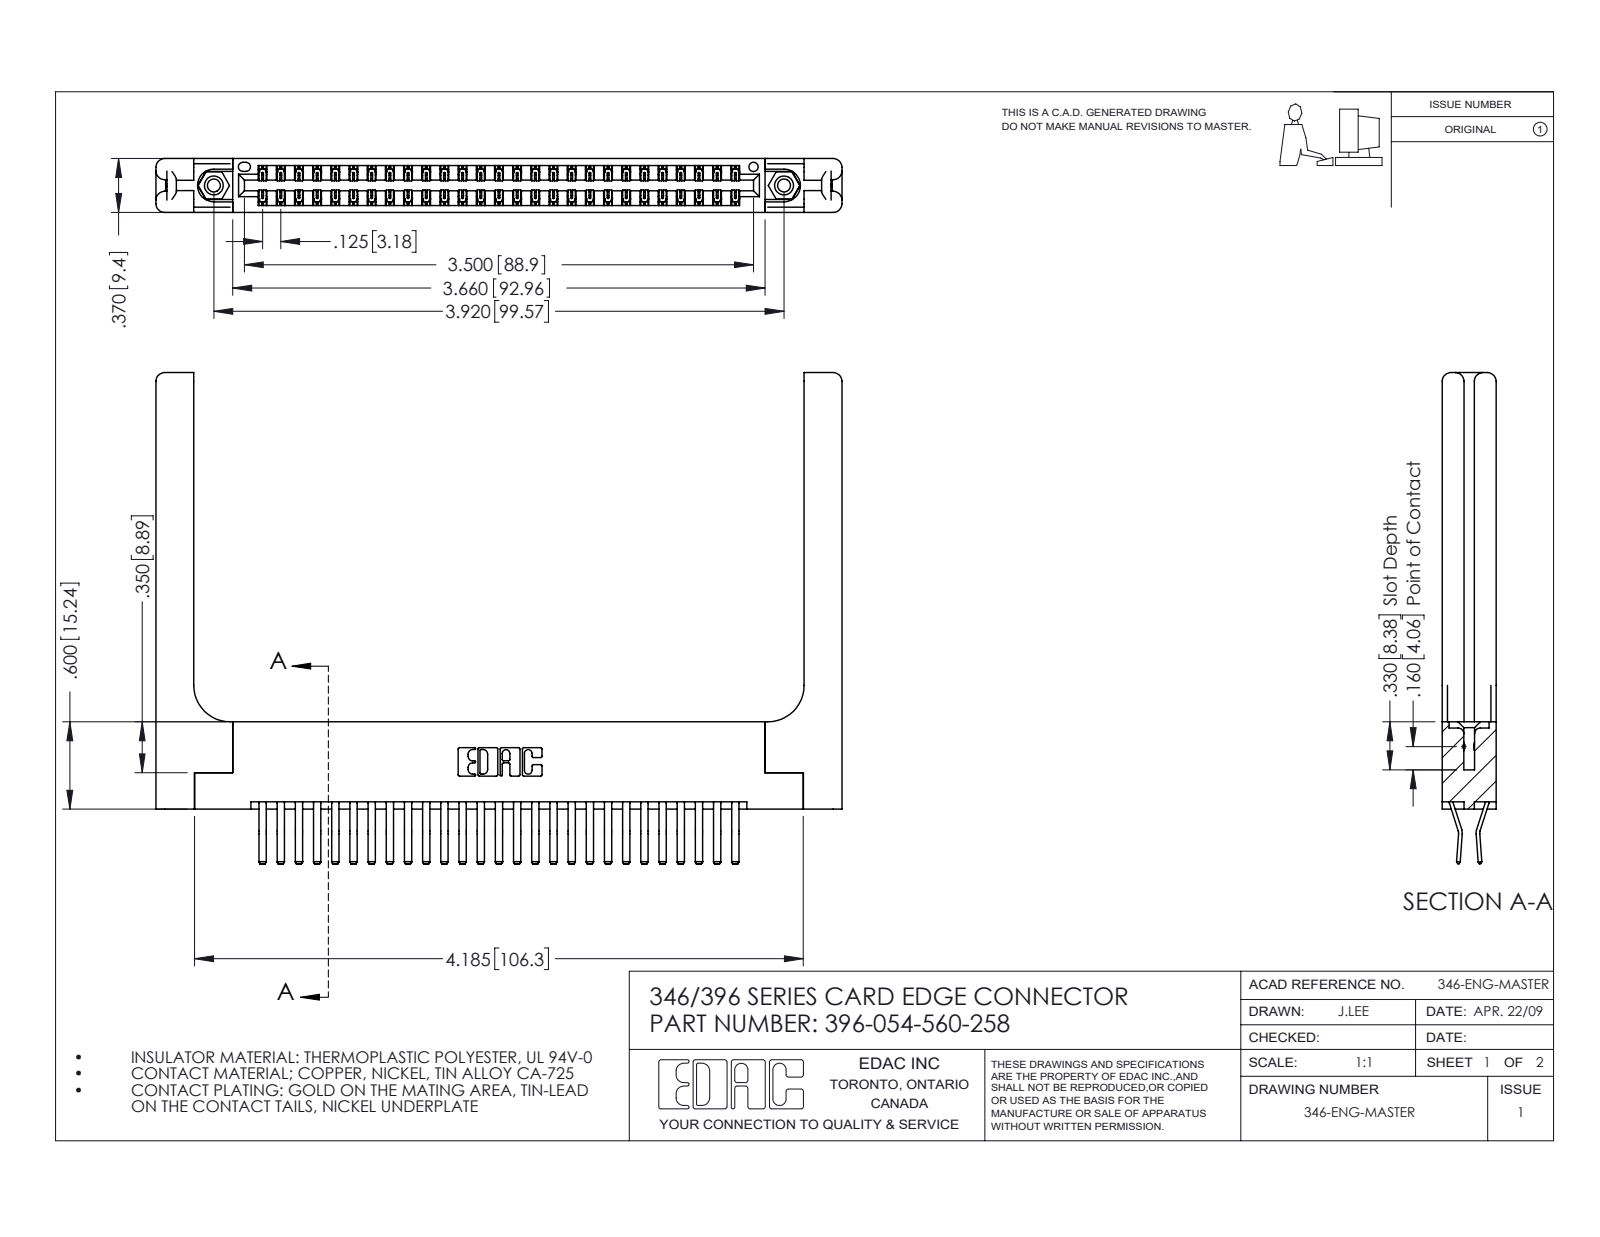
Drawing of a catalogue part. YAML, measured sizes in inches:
part_name: "346-220-058_345-220-058; 345-250-001_345-250-001-102; 345-292-001_560 Tail; 346 Part_Flush Mounting Lugs - 0.156 Dia-TH (+1 more)"
step_written_by: "SolidWorks 2016 (CONFIG_CONTROL_DESIGN)"
units: inches
bodies: {solids: 59, faces: 3294, planar: 2114, cylindrical: 1120, other: 60}
overall_size: [4.716, 3.375, 0.37]
volume: 1.185
surface_area: 34.2
round_holes:
  - {diameter: 0.089, count: 2}
  - {diameter: 0.125, count: 2}
  - {diameter: 0.156, count: 2}
  - {diameter: 0.064, count: 1}
round_bosses_or_shafts:
  - {diameter: 0.155, count: 2}
partial_cylinders:
  - {radius: 0.006, count: 81}
  - {radius: 0.01, count: 22}
  - {radius: 0.06, count: 16}
  - {radius: 0.007, count: 6}
  - {radius: 0.031, count: 6}
  - {radius: 0.026, count: 3}
  - {radius: 0.01, count: 2}
  - {radius: 0.014, count: 2}
face_to_face_distances: [0.37, 0.072, 0.048, 0.322, 0.148, 0.15, 0.025, 0.25, 0.298, 0.275]
hole_center_spacings: [0.246, 3.712, 3.92]
